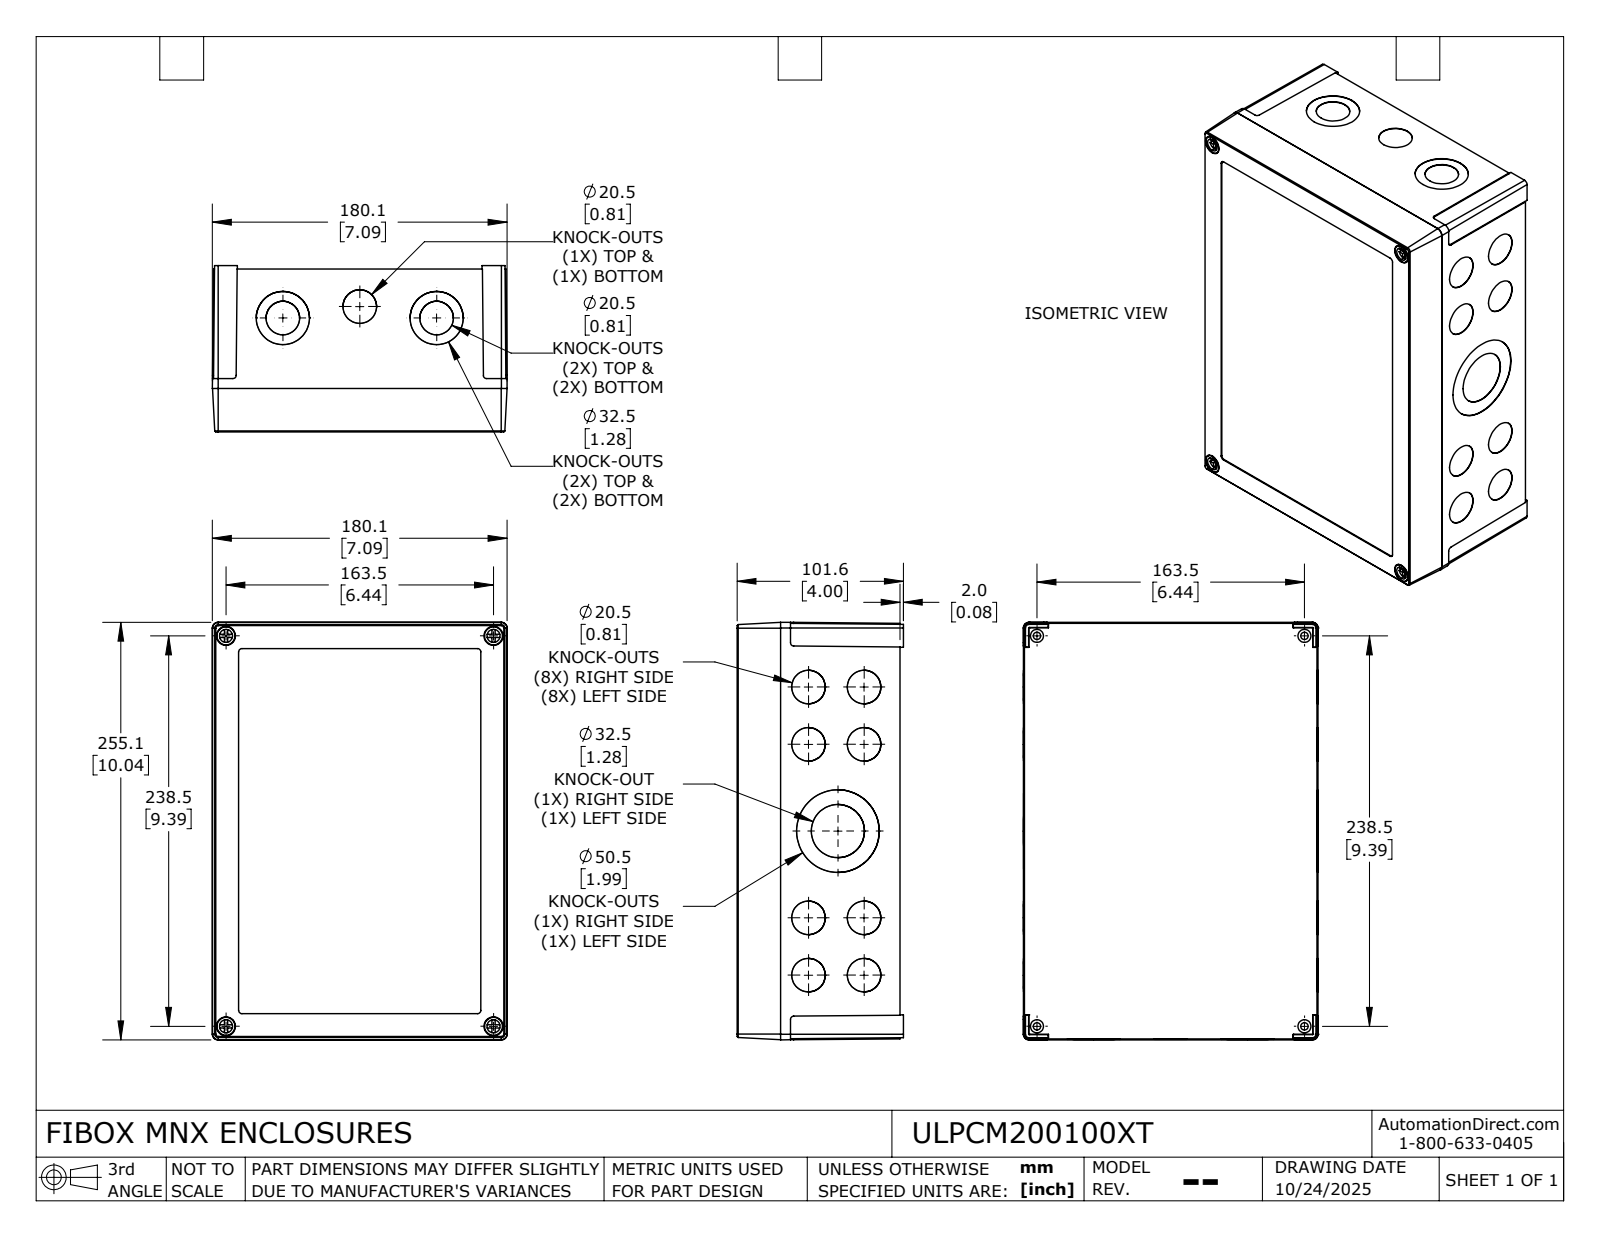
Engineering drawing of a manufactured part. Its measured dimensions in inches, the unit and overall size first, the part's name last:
Units: inches
Overall size (bounding box): 10.043 × 7.091 × 4
Round holes (diameter × count): ⌀0.807 ×22, ⌀0.126 ×20, ⌀0.157 ×20, ⌀1.28 ×6, ⌀0.177 ×4, ⌀0.315 ×4, ⌀0.457 ×4, ⌀1.988 ×2
Round bosses / shafts (diameter × count): ⌀0.315 ×16, ⌀0.098 ×8, ⌀0.433 ×4, ⌀0.283 ×4, ⌀0.276 ×4
Partial cylindrical surfaces — rounded edges, fillets, slot ends (radius × count): R0.079 ×8, R0.112 ×6, R0.042 ×4, R0.197 ×4, R0.046 ×2
Main face-to-face distances: 3.815, 0.165, 0.118, 3.697, 0.087, 3.902, 3.783, 3.921, 3.803, 0.02
Hole centre spacings: 1.378, 1.339, 1.921, 1.939, 5.046, 5.551, 5.71, 4.921
Volume: 36.22 in³ · Surface area: 568 in²
Bodies: 6 solids, 720 faces (392 planar, 284 cylindrical, 44 other)
Part name (STEP PRODUCT): ULPCM200100XT_Default
STEP written by: SolidWorks 2024 (CONFIG_CONTROL_DESIGN)
